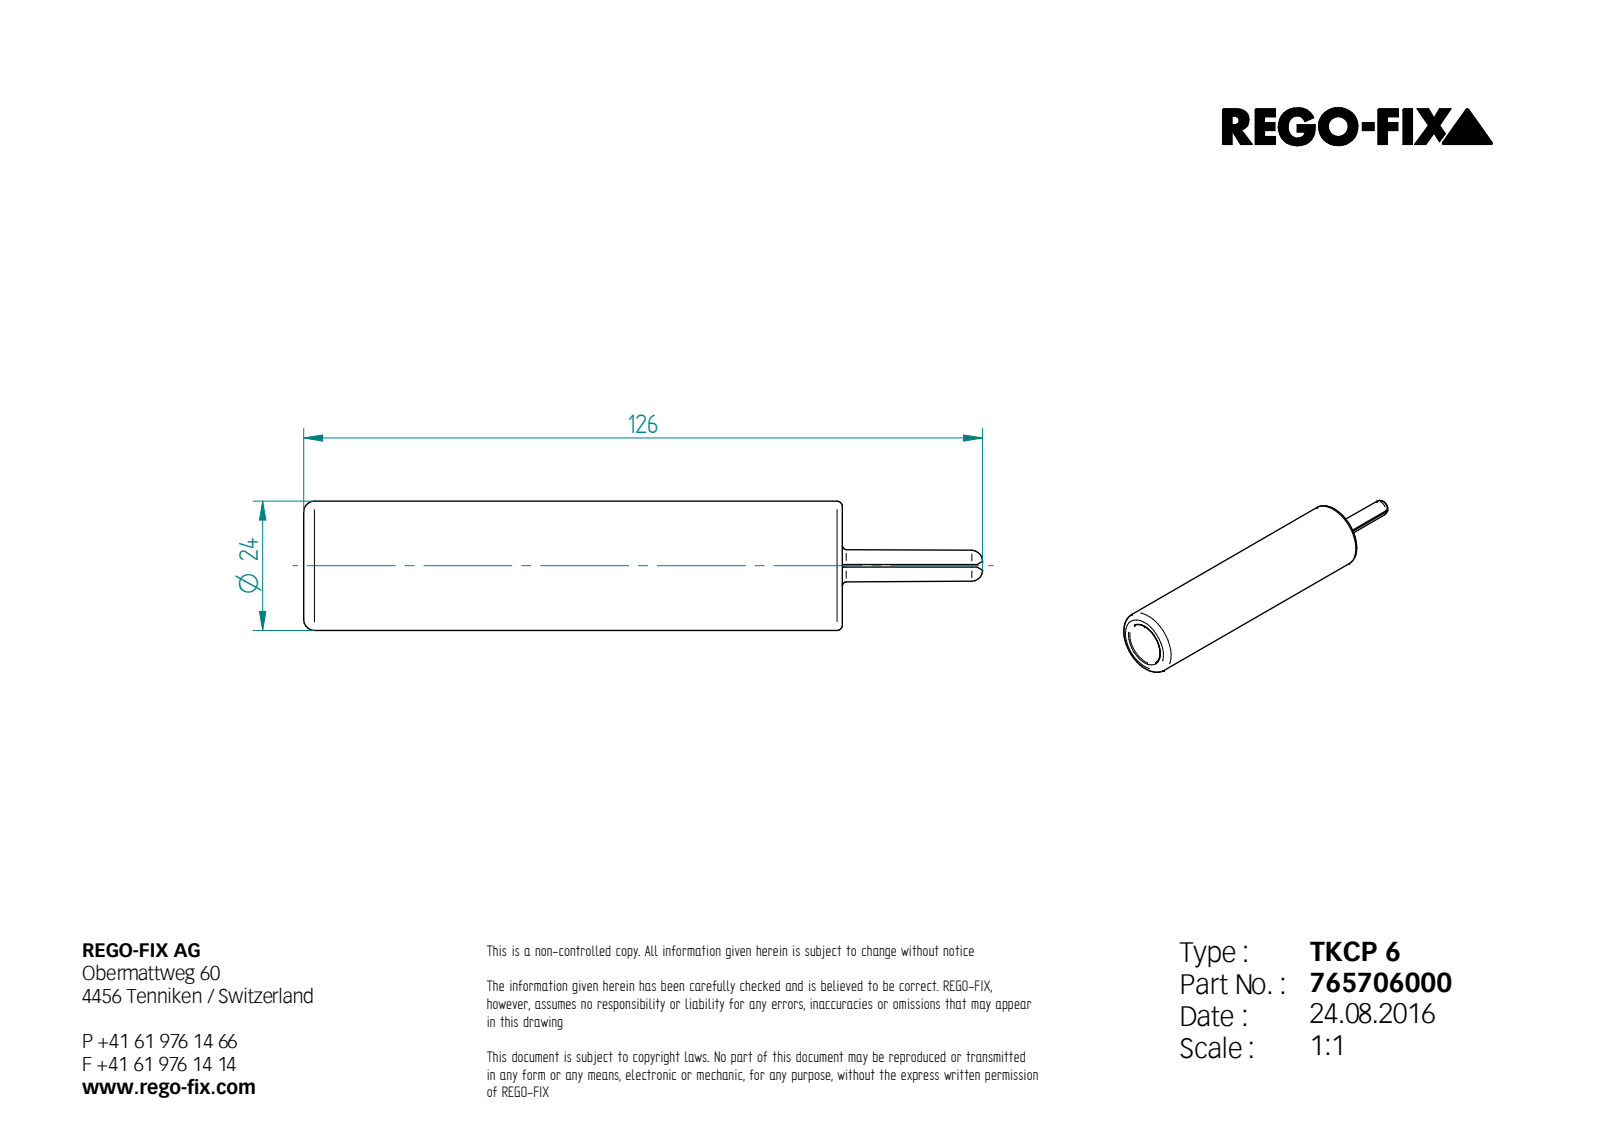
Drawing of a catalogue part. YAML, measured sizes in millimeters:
part_name: "0003777"
step_written_by: "ST-DEVELOPER v16.7 (AUTOMOTIVE_DESIGN)"
units: millimeters
bodies: {solids: 1, faces: 21, planar: 8, cylindrical: 1, other: 12}
overall_size: [76.3, 15.99, 15.99]
volume: 6681
surface_area: 4955
partial_cylinders:
  - {radius: 0.25, count: 1}
face_to_face_distances: [0.5, 6, 32.3, 26.3]
